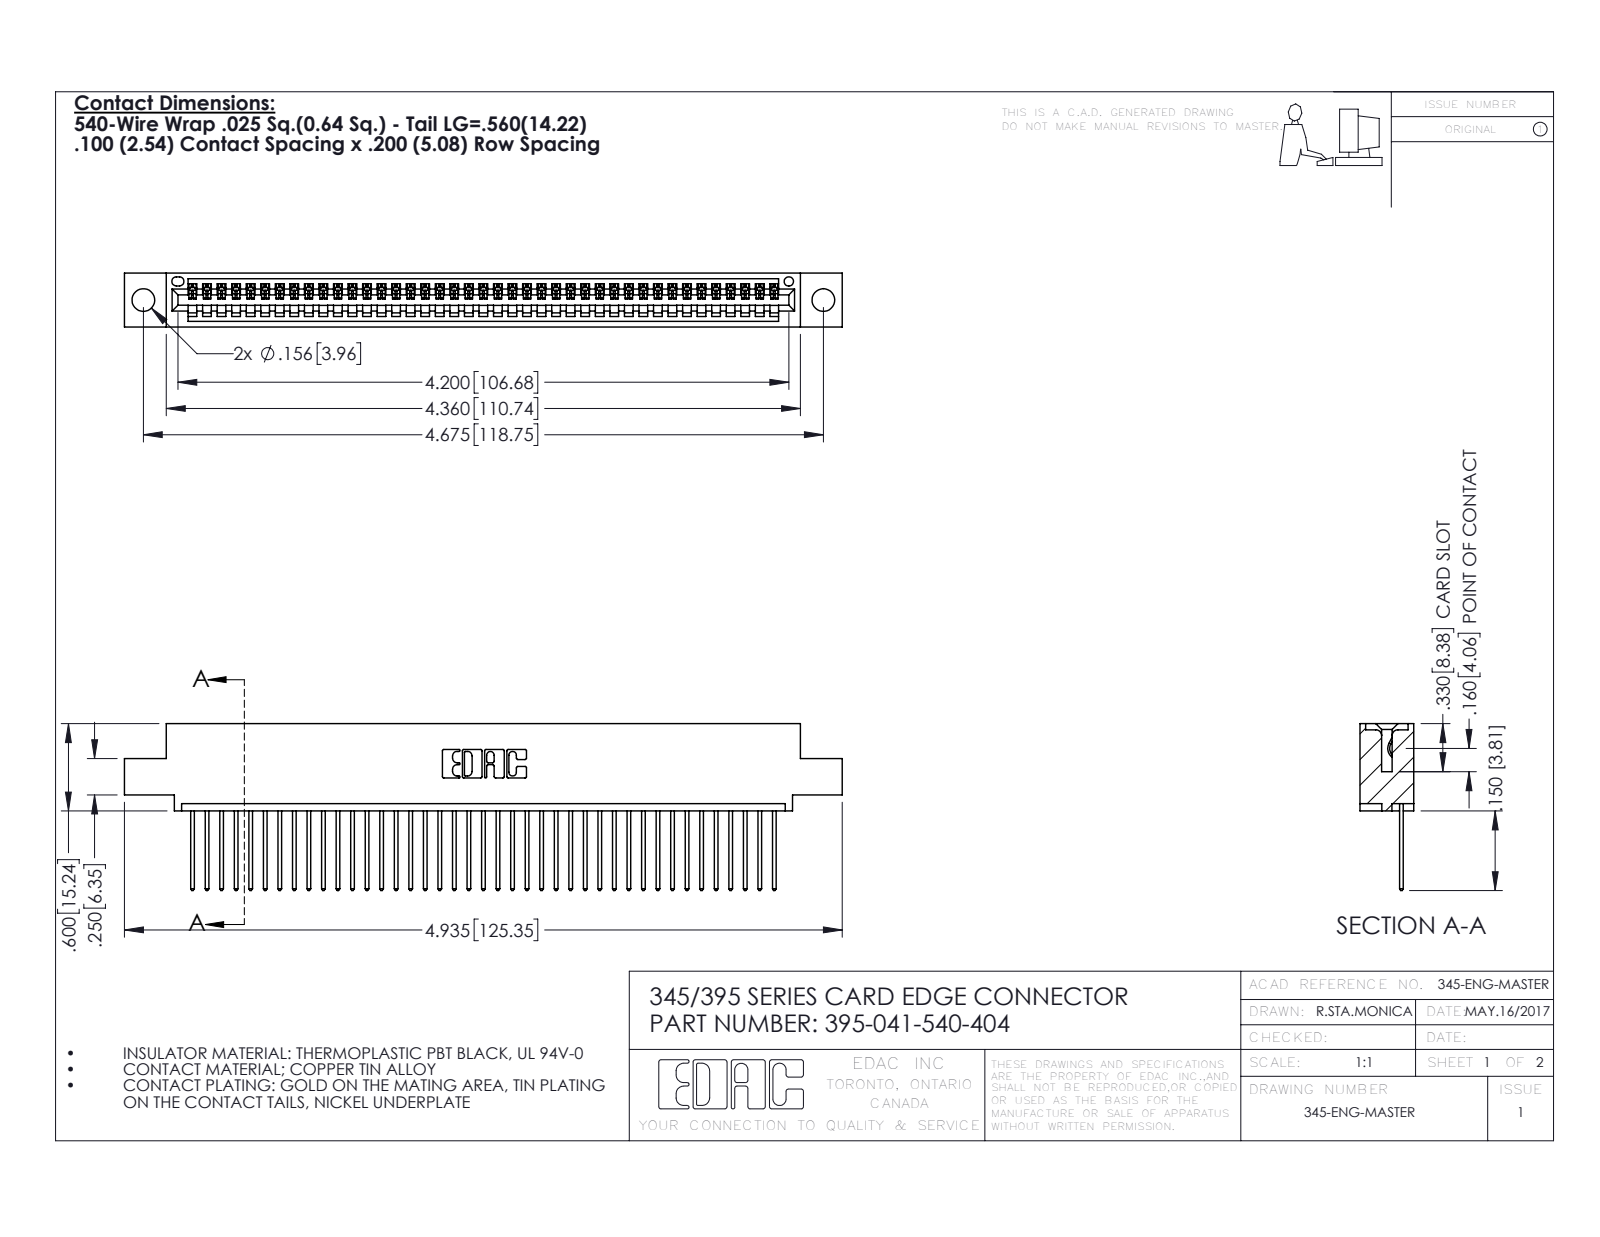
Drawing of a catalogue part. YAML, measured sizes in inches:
part_name: "395-041-540-404; 345 Part_0.110 Offset - 0.156 Dia-TH; 345-292-001_345-293-140"
step_written_by: "SolidWorks 2016 (CONFIG_CONTROL_DESIGN)"
units: inches
bodies: {solids: 42, faces: 2508, planar: 1724, cylindrical: 784, other: 0}
overall_size: [4.935, 1.147, 0.37]
volume: 0.72
surface_area: 24.72
round_holes:
  - {diameter: 0.156, count: 2}
  - {diameter: 0.064, count: 1}
partial_cylinders:
  - {radius: 0.006, count: 82}
  - {radius: 0.01, count: 82}
  - {radius: 0.01, count: 22}
  - {radius: 0.007, count: 6}
  - {radius: 0.031, count: 6}
  - {radius: 0.026, count: 3}
  - {radius: 0.031, count: 2}
  - {radius: 0.04, count: 2}
face_to_face_distances: [0.298, 0.072, 0.37, 0.098, 0.272, 0.025, 0.2, 0.225, 0.149, 0.072]
hole_center_spacings: [0.27, 4.439, 4.675]
